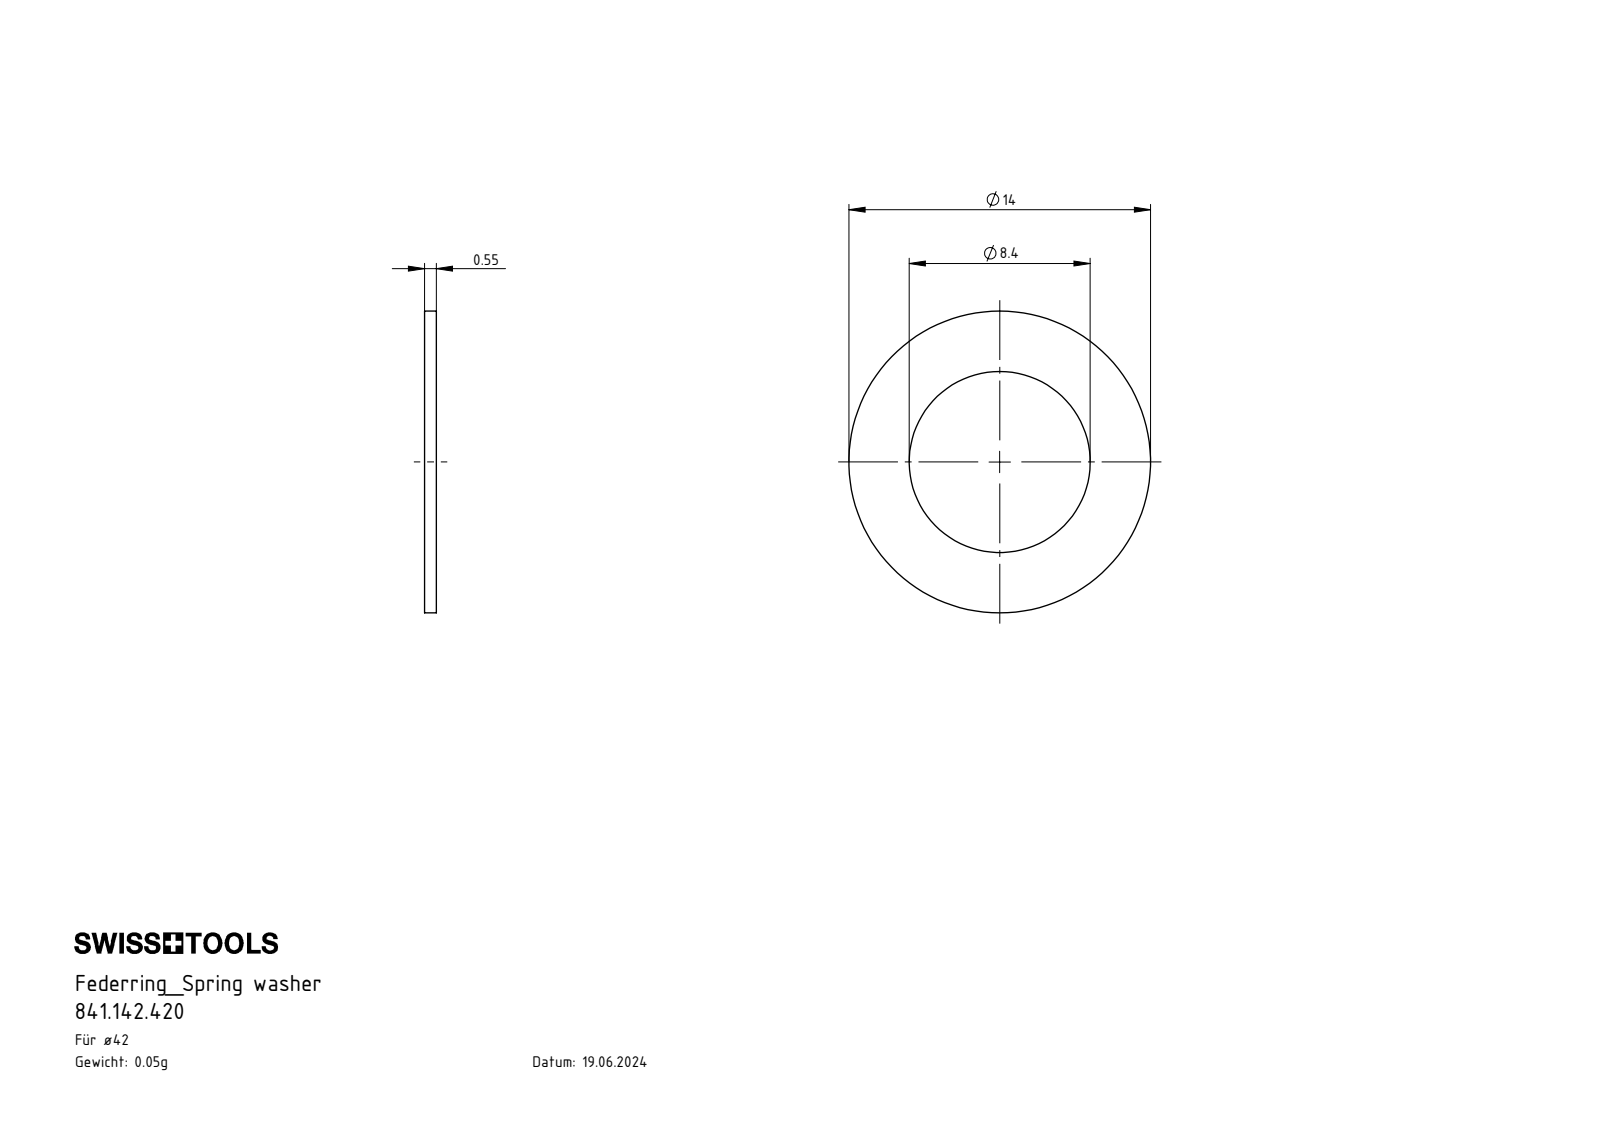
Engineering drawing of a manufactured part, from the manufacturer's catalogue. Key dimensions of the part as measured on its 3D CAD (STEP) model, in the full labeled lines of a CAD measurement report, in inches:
Part name (STEP PRODUCT): 841.142.420
STEP written by: SolidWorks 2022 (AUTOMOTIVE_DESIGN)
Units: inches
Bodies: 1 solid, 6 faces (2 planar, 4 cylindrical, 0 other)
Overall size (bounding box): 0.551 × 0.551 × 0.022
Volume: 0.003 in³ · Surface area: 0.366 in²
Round holes (diameter × count): ⌀0.331 ×1
Round bosses / shafts (diameter × count): ⌀0.551 ×1
Main face-to-face distances: 0.022
